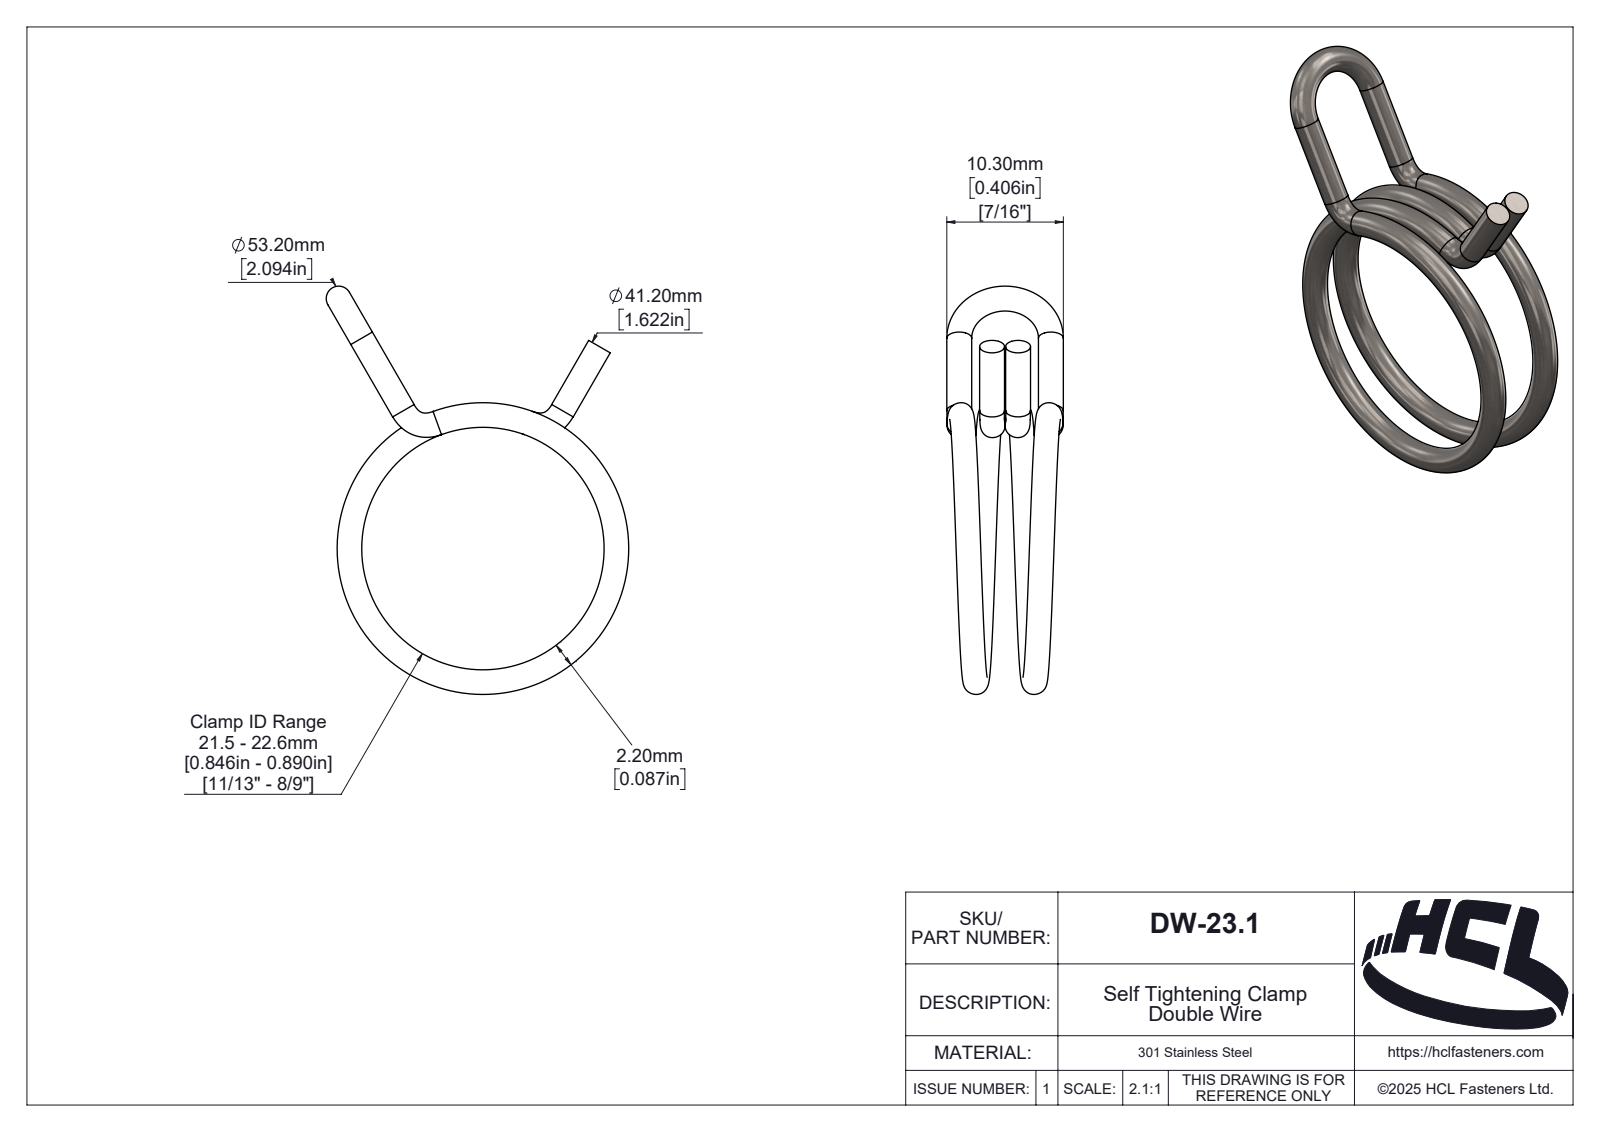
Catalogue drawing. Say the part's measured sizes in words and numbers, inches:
The part is named "DW-23.1". Its 3-D file was written by "SolidWorks 2025 (AUTOMOTIVE_DESIGN)". It is 1 solid with 132 faces: 14 planar, 53 cylindrical and 65 other. Overall it measures 1.42 by 1.053 by 0.406 inches. Its volume is 0.05 cubic inches and its surface area 2.348 square inches. Round bosses or shafts: 4 of diameter 0.087. Partial cylindrical surfaces (rounded edges, fillets, slot ends): 1 of radius 0.006, 1 of radius 0.008, 1 of radius 0.008, 1 of radius 0.01, 1 of radius 0.014, 1 of radius 0.019, 1 of radius 0.024, 1 of radius 0.027.
